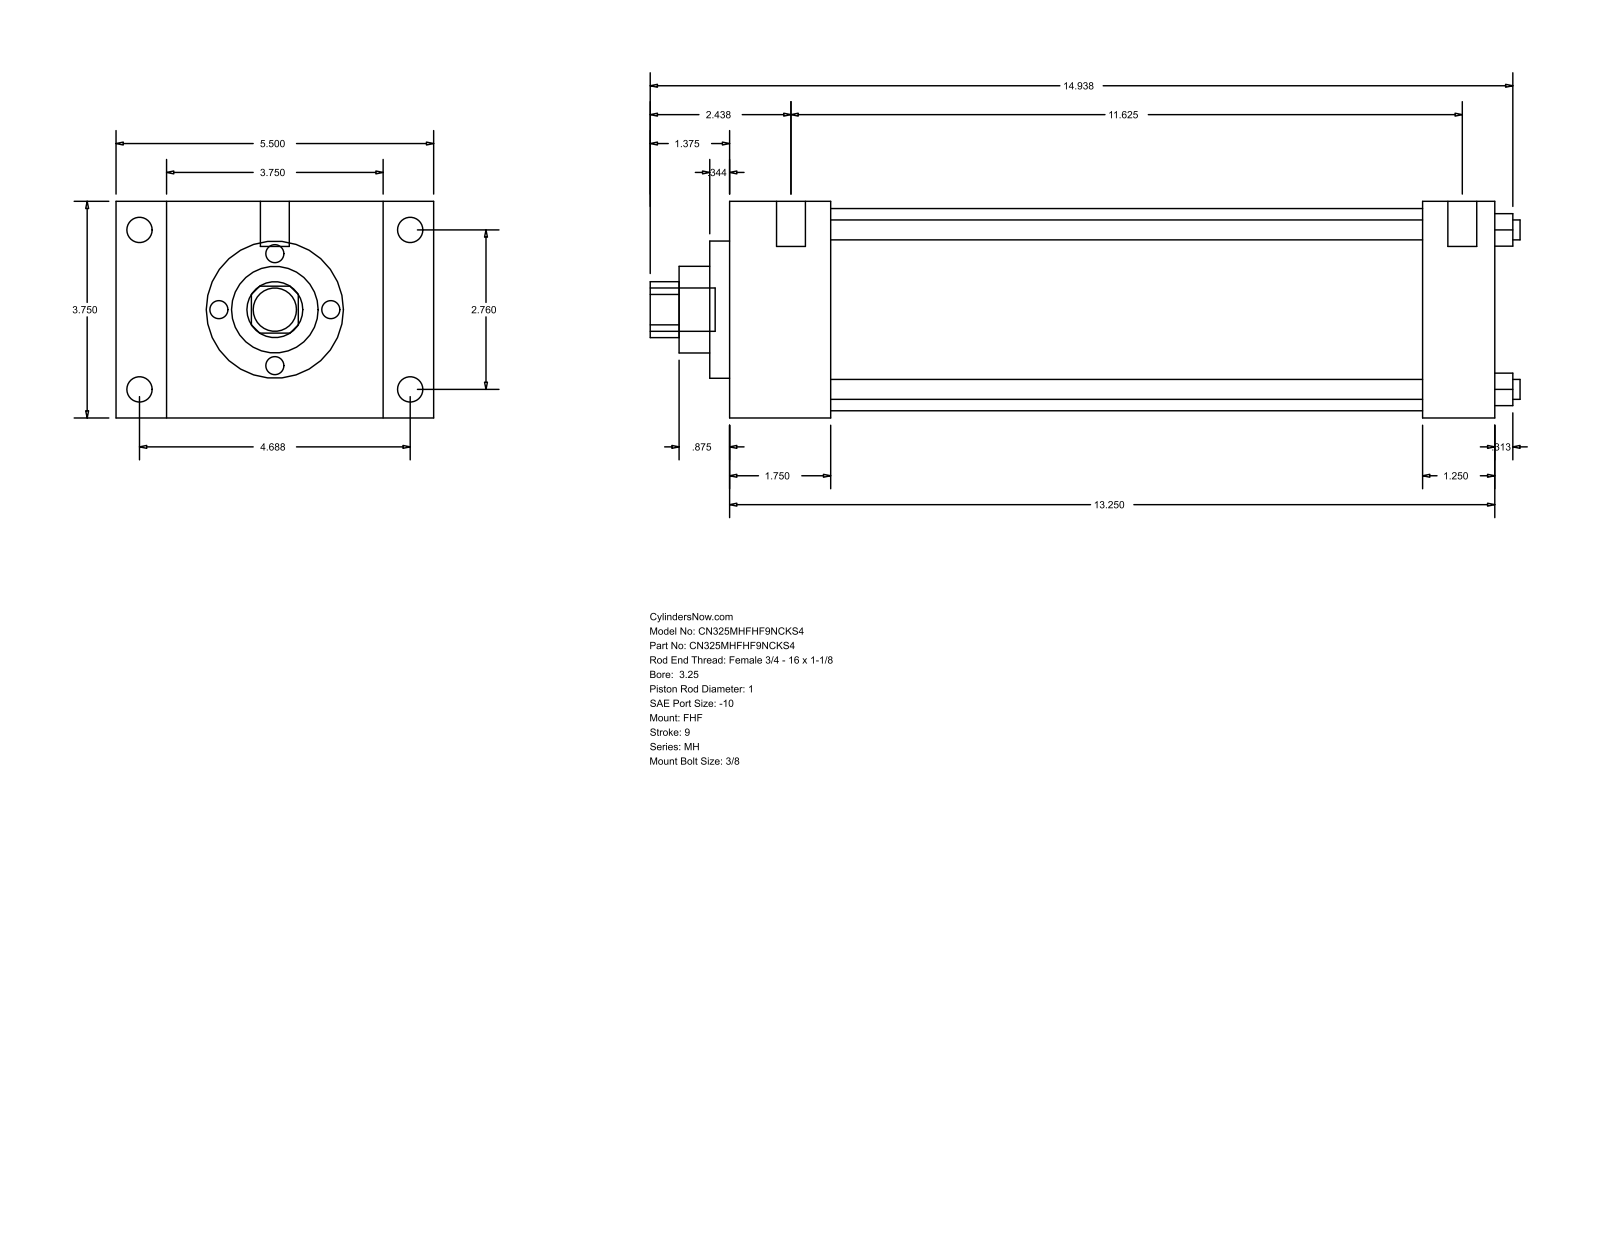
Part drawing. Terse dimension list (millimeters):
name: MH_FHF__0325_1
written by: GSSL Pune (CONFIG_CONTROL_DESIGN)
unit: mm
bodies: 0 solids, 90 faces (61 planar, 29 cylindrical, 0 other)
size: 382.59 × 139.7 × 95.25
holes: 4× ⌀8.76, 1× ⌀25.4, 1× ⌀38.1, 1× ⌀60.33, 1× ⌀88.9
bosses: 4× ⌀11.13, 4× ⌀5.56, 2× ⌀12.7, 1× ⌀19.05
rounds: 1× R12.29
face distances: 95.24, 336.56, 44.46, 292.1, 22.23, 117.47, 139.7, 304.81, 260.35, 31.75
hole spacings: 49.57, 70.1, 99.14
